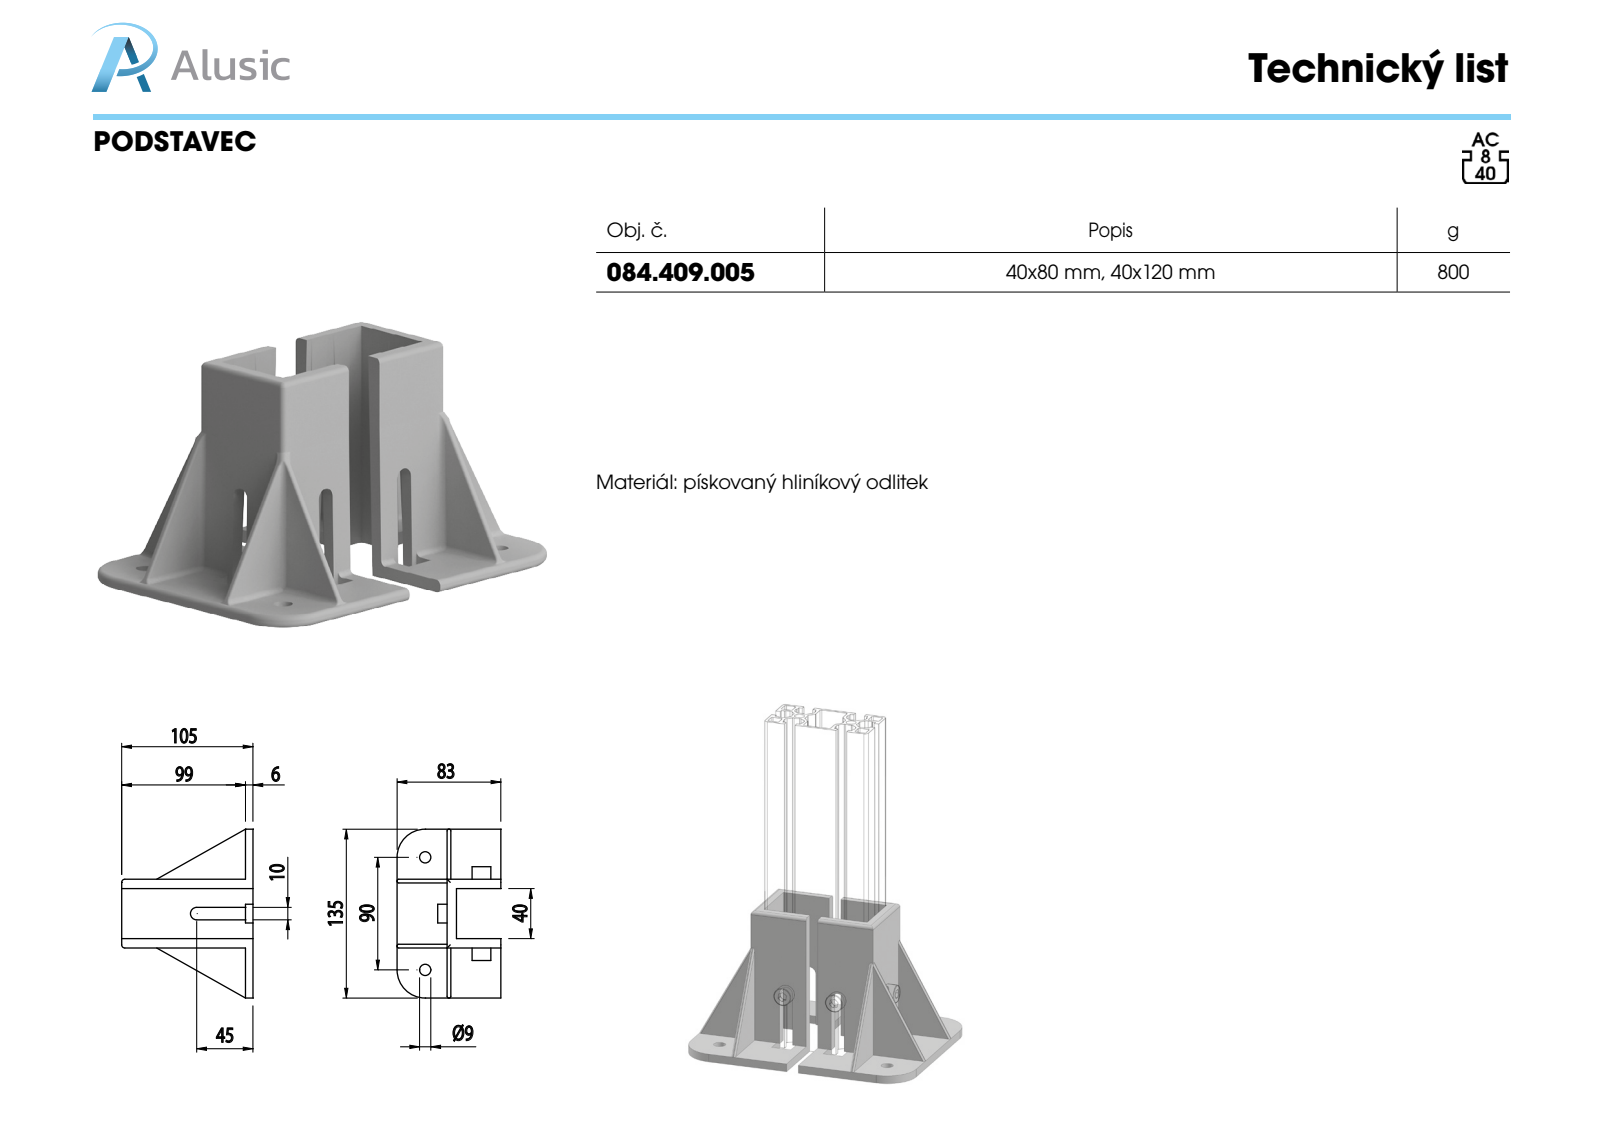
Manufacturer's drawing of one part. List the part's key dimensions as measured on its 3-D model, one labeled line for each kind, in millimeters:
Part name (STEP PRODUCT): 084.409.005
STEP written by: SolidWorks 2011 (CONFIG_CONTROL_DESIGN)
Units: millimetres
Bodies: 1 solid, 71 faces (51 planar, 20 cylindrical, 0 other)
Overall size (bounding box): 135 × 105 × 83
Volume: 152 693 mm³ · Surface area: 58 183 mm²
Round holes (diameter × count): ⌀9 ×2
Partial cylindrical surfaces — rounded edges, fillets, slot ends (radius × count): R1.2 ×8, R2.5 ×3, R5 ×2, R22.5 ×2
Main face-to-face distances: 7.5, 6, 47.5, 40, 3, 4.5, 55, 43, 52, 44.5
Hole centre spacings: 90
